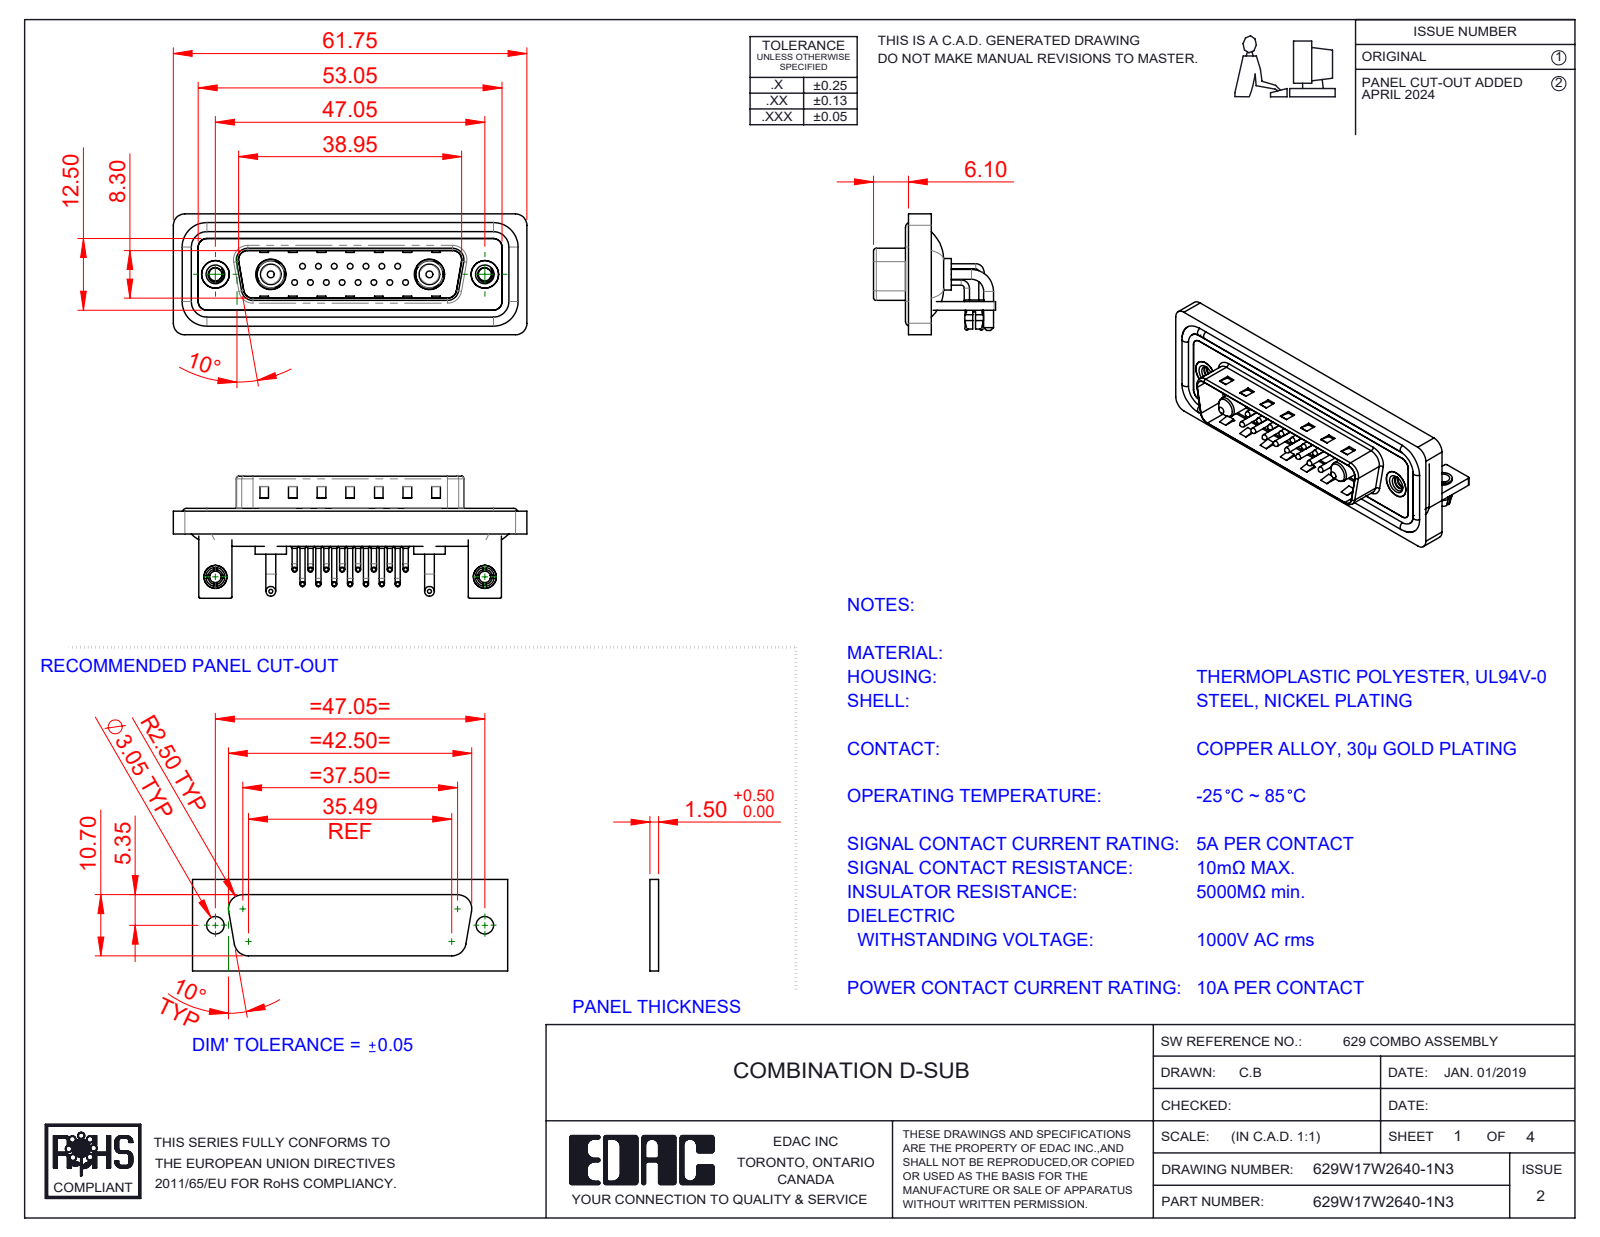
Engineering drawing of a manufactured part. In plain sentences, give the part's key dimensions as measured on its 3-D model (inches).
The part is named "629Combo Stabilizer Bracket; 629Combo Waterproof Housing_25 Contacts; 629Combo Board Lock; 629Combo Contact Row 1 (+7 more)". Its 3-D file was written by "SolidWorks 2023 (CONFIG_CONTROL_DESIGN)". It is 30 solids with 2351 faces: 1257 planar, 820 cylindrical and 274 other. Overall it measures 2.431 by 0.839 by 0.831 inches. Its volume is 0.47 cubic inches and its surface area 20.61 square inches. Round holes: 17 of diameter 0.079, 15 of diameter 0.03, 15 of diameter 0.063, 2 of diameter 0.089, 2 of diameter 0.098, 2 of diameter 0.126, 2 of diameter 0.157, 2 of diameter 0.189, 2 of diameter 0.191, 2 of diameter 0.197, 2 of diameter 0.209. Round bosses or shafts: 30 of diameter 0.035, 15 of diameter 0.059, 15 of diameter 0.039, 15 of diameter 0.026, 4 of diameter 0.067, 4 of diameter 0.063, 2 of diameter 0.217, 2 of diameter 0.205. Partial cylindrical surfaces (rounded edges, fillets, slot ends): 19 of radius 0.079, 18 of radius 0.059, 16 of radius 0.01, 15 of radius 0.04, 9 of radius 0.02, 8 of radius 0.063, 4 of radius 0.024, 4 of radius 0.026. The main face-to-face distances are 0.016, 0.031, 0.059, 0.083, 0.114, 0.043, 0.161, 0.063, 0.177, 0.146. The hole center spacings are 0.124, 0.109, 0.218, 0.327, 0.198, 0.295, 0.436, 0.198.
